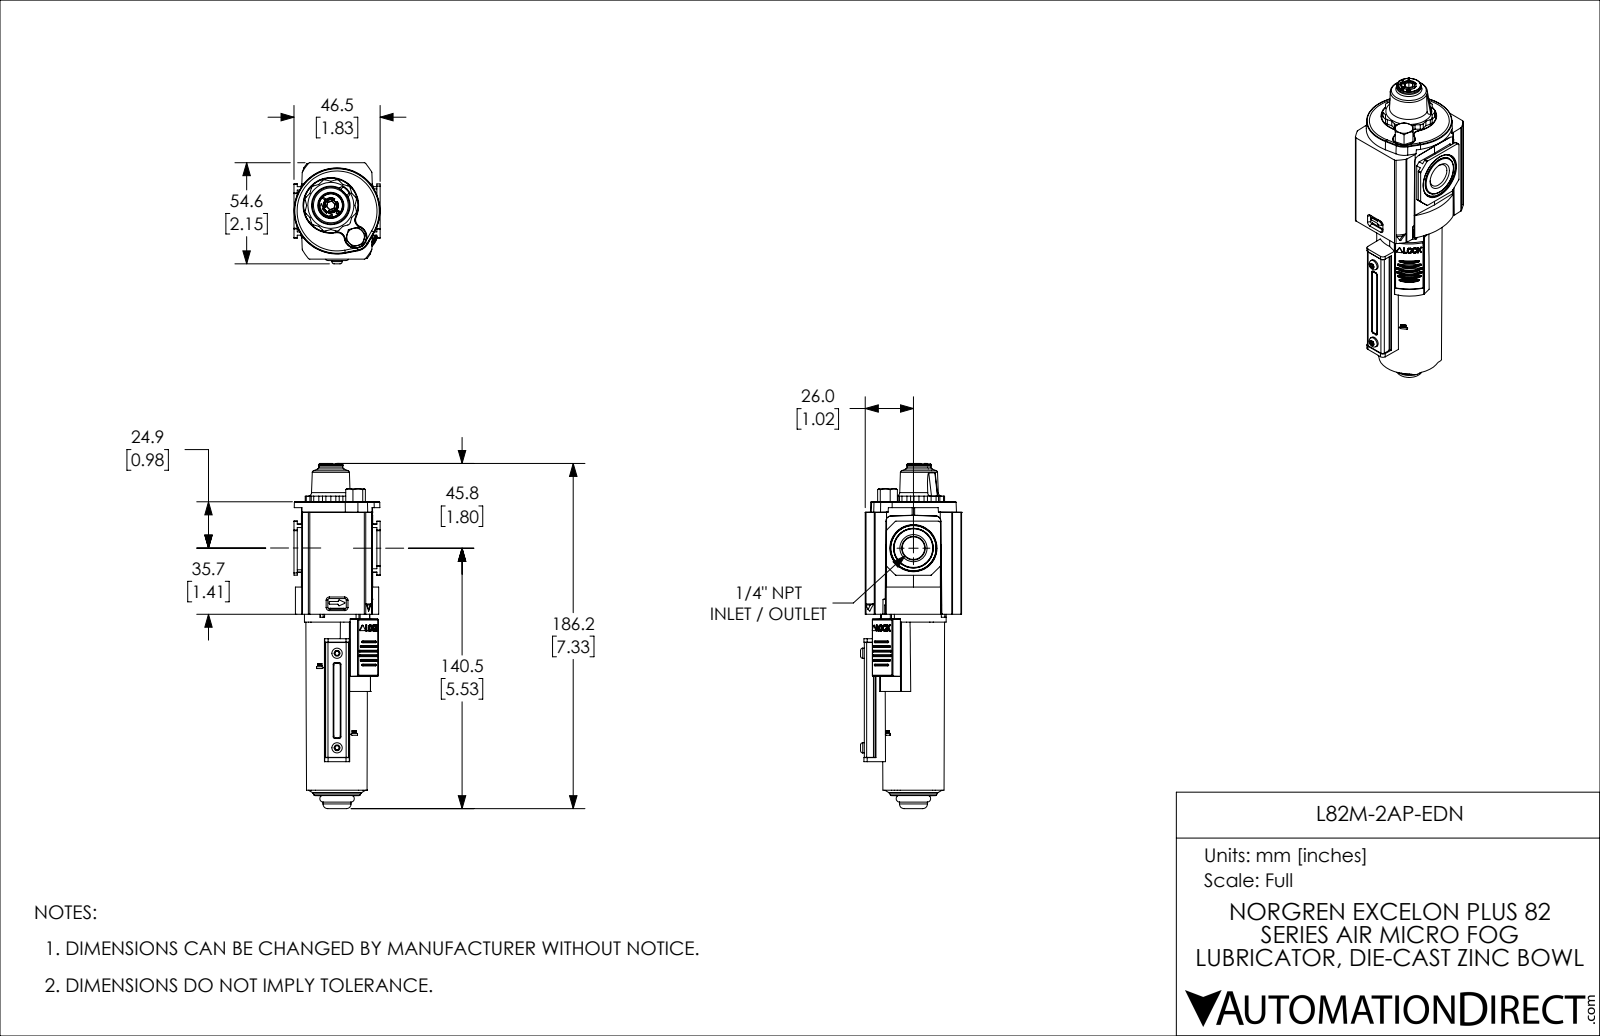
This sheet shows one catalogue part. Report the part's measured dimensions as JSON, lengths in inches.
{"part_name": "L82M-2AP-EDN", "step_written_by": "SolidWorks 2021 (CONFIG_CONTROL_DESIGN)", "units": "inches", "bodies": {"solids": 7, "faces": 1276, "planar": 576, "cylindrical": 469, "other": 231}, "overall_size": [7.331, 2.148, 1.831], "volume_in3": 12.59, "surface_area_in2": 95.53, "round_holes": [[0.271, 1], [0.312, 1], [0.312, 1], [0.354, 1], [0.628, 1], [0.943, 1], [1.181, 1]], "round_bosses_or_shafts": [[0.24, 2], [0.217, 2], [1.388, 1], [1.356, 1], [1.291, 1], [1.257, 1], [1.161, 1], [0.906, 1]], "partial_cylinders_radius": [[0.02, 53], [0.039, 38], [0.008, 16], [0.01, 12], [0.011, 12], [0.019, 12], [0.075, 12], [0.118, 9]], "face_to_face_distances": [0.059, 1.988, 2.047, 1.929, 0.236, 1.352, 0.182, 1.475, 1.417, 1.293], "hole_center_spacings": [0.177, 0.677, 0.851]}
